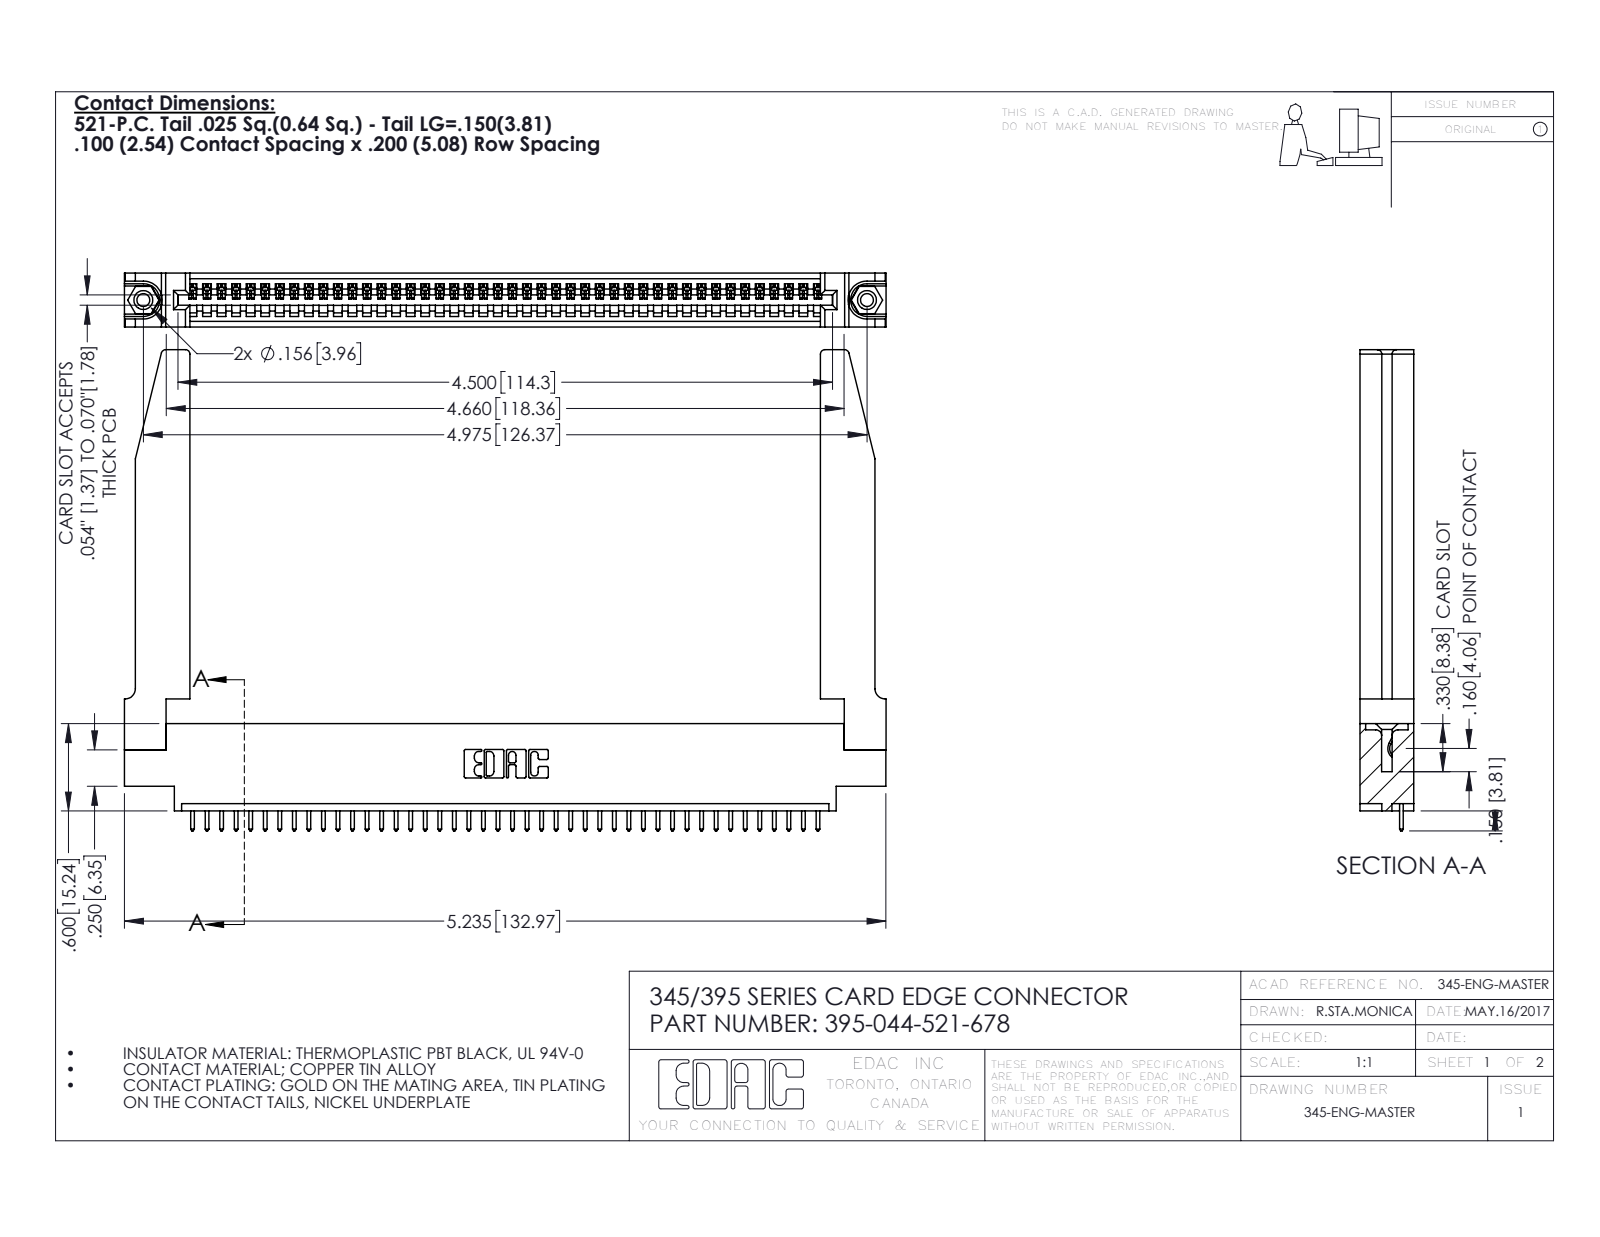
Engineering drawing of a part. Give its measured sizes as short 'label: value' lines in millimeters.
name: 345-220-078_345-220-078; 395-044-521-678; 345-292-001_345-293-121; 345 Part_0.170 Offset - 0.156 Dia-TH (+1 more)
written by: SolidWorks 2016 (CONFIG_CONTROL_DESIGN)
unit: mm
bodies: 49 solids, 2916 faces (1986 planar, 878 cylindrical, 52 other)
size: 133 × 84 × 9.4
volume: 20 170 mm³; area: 23 000 mm²
holes: 2× ⌀2.3, 2× ⌀3.2, 2× ⌀4, 1× ⌀1.6
bosses: 2× ⌀3.9
rounds: 88× R0.2, 88× R0.3, 22× R0.3, 8× R0.8, 6× R0.2, 6× R0.8, 3× R0.7, 2× R0.8
face distances: 9.4, 1.8, 7.6, 5.1, 2.5, 6.9, 0.6, 5.7, 3.8, 3.8
hole spacings: 6.9, 120.4, 126.4
